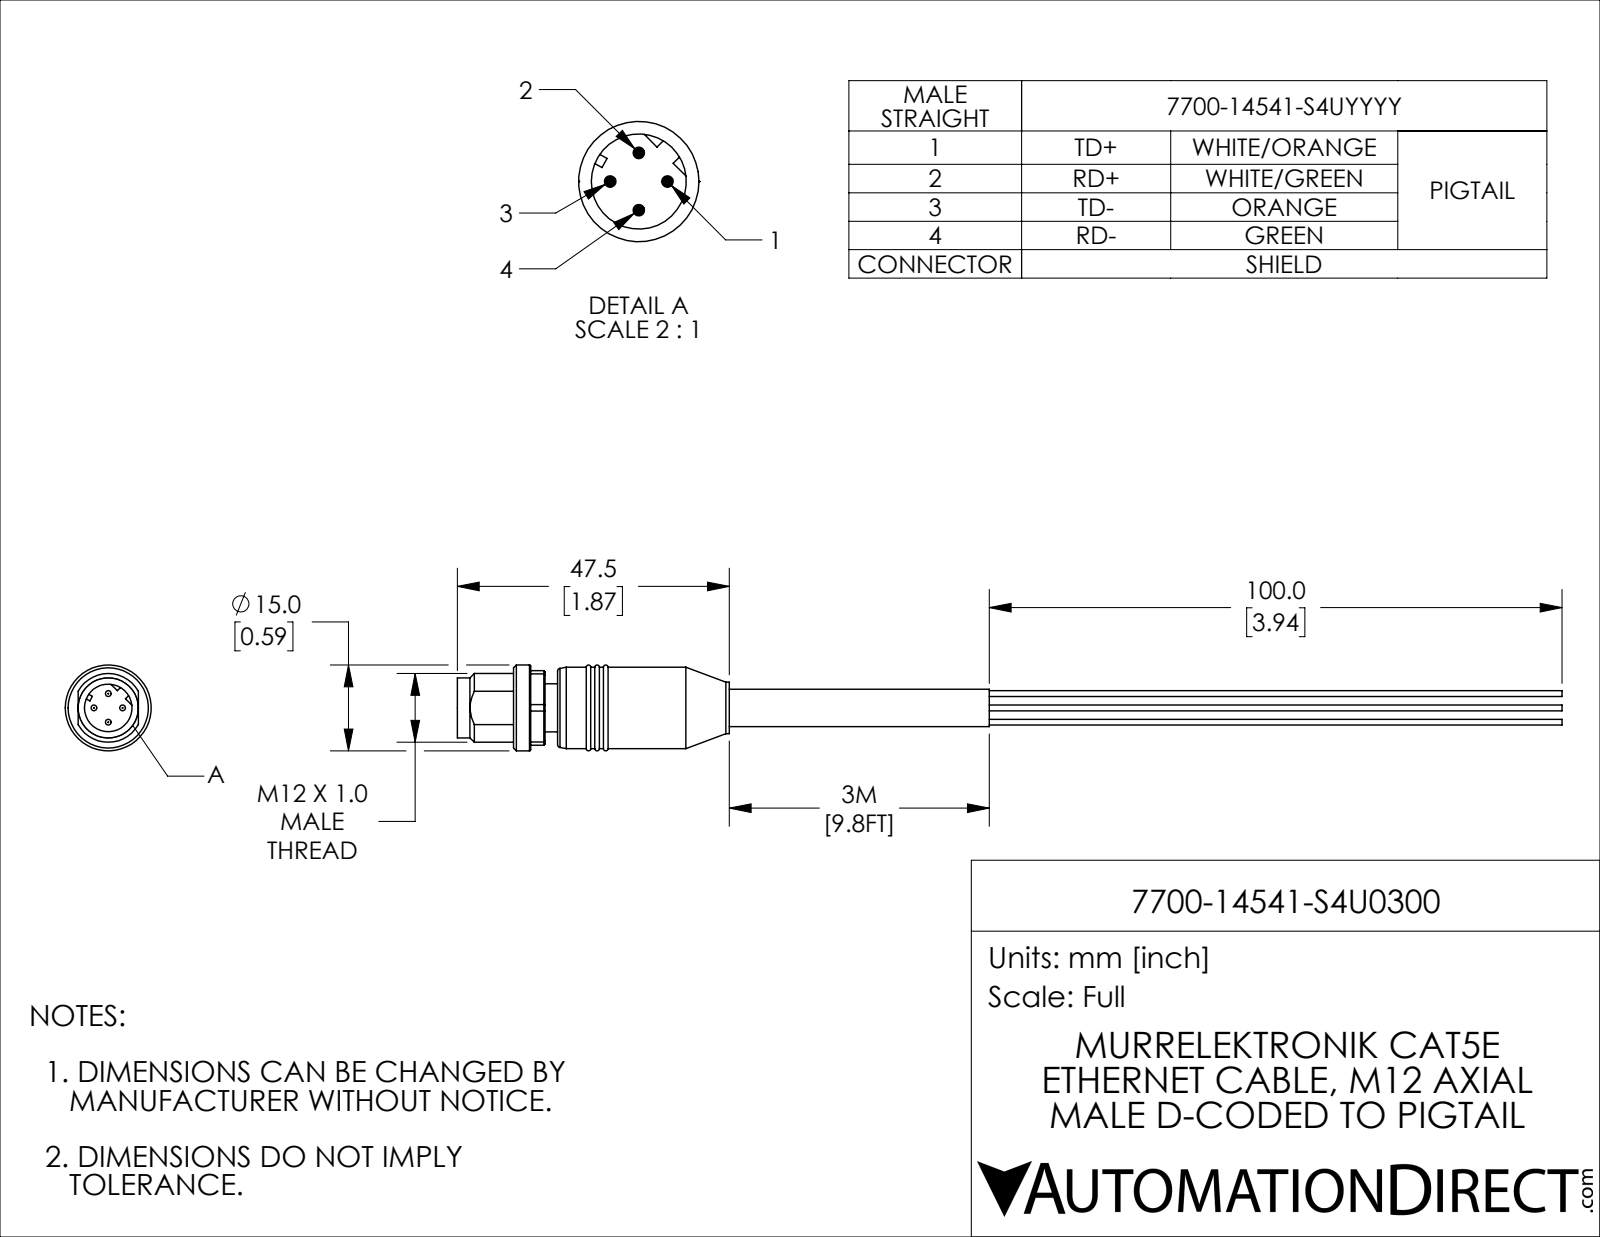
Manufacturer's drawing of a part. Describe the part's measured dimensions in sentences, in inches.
The part is named "7700-14541-S4U0300". Its 3-D file was written by "SolidWorks 2021 (CONFIG_CONTROL_DESIGN)". It is 1 solid with 125 faces: 40 planar, 45 cylindrical and 40 other. Overall it measures 7.594 by 0.591 by 0.591 inches. Its volume is 0.473 cubic inches and its surface area 7.675 square inches. Round holes: 1 of diameter 0.327. Round bosses or shafts: 4 of diameter 0.039, 1 of diameter 0.591, 1 of diameter 0.559, 1 of diameter 0.413, 1 of diameter 0.354, 1 of diameter 0.331, 1 of diameter 0.256. Partial cylindrical surfaces (rounded edges, fillets, slot ends): 1 of radius 0.236, 1 of radius 0.283. The main face-to-face distances are 0.087, 0.035, 0.252, 0.339, 0.217, 0.303, 0.512, 0.413, 0.35, 0.386.
